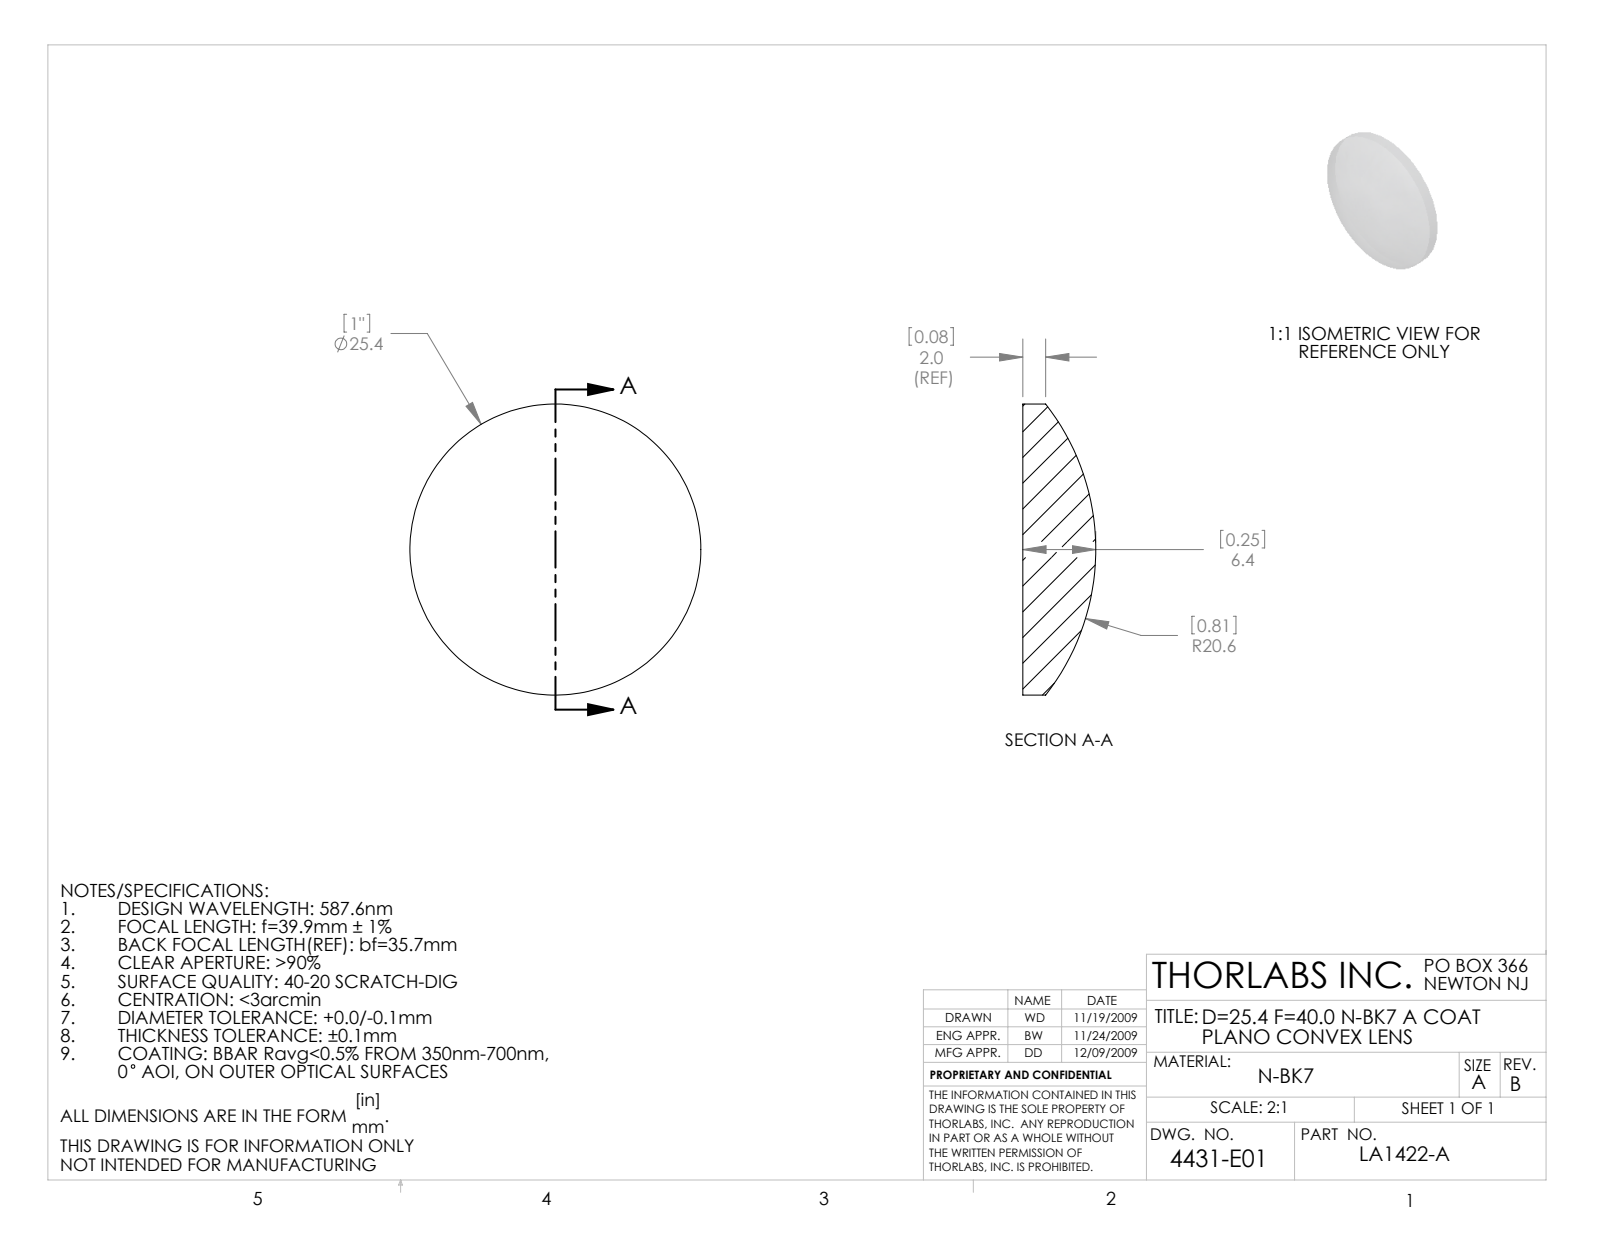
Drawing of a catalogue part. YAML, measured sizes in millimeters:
part_name: "4431-E0W"
step_written_by: "SolidWorks 2009 (AUTOMOTIVE_DESIGN)"
units: millimeters
bodies: {solids: 1, faces: 5, planar: 1, cylindrical: 2, other: 2}
overall_size: [25.4, 25.4, 6.37]
volume: 2162
surface_area: 1232
round_bosses_or_shafts:
  - {diameter: 25.4, count: 1}
